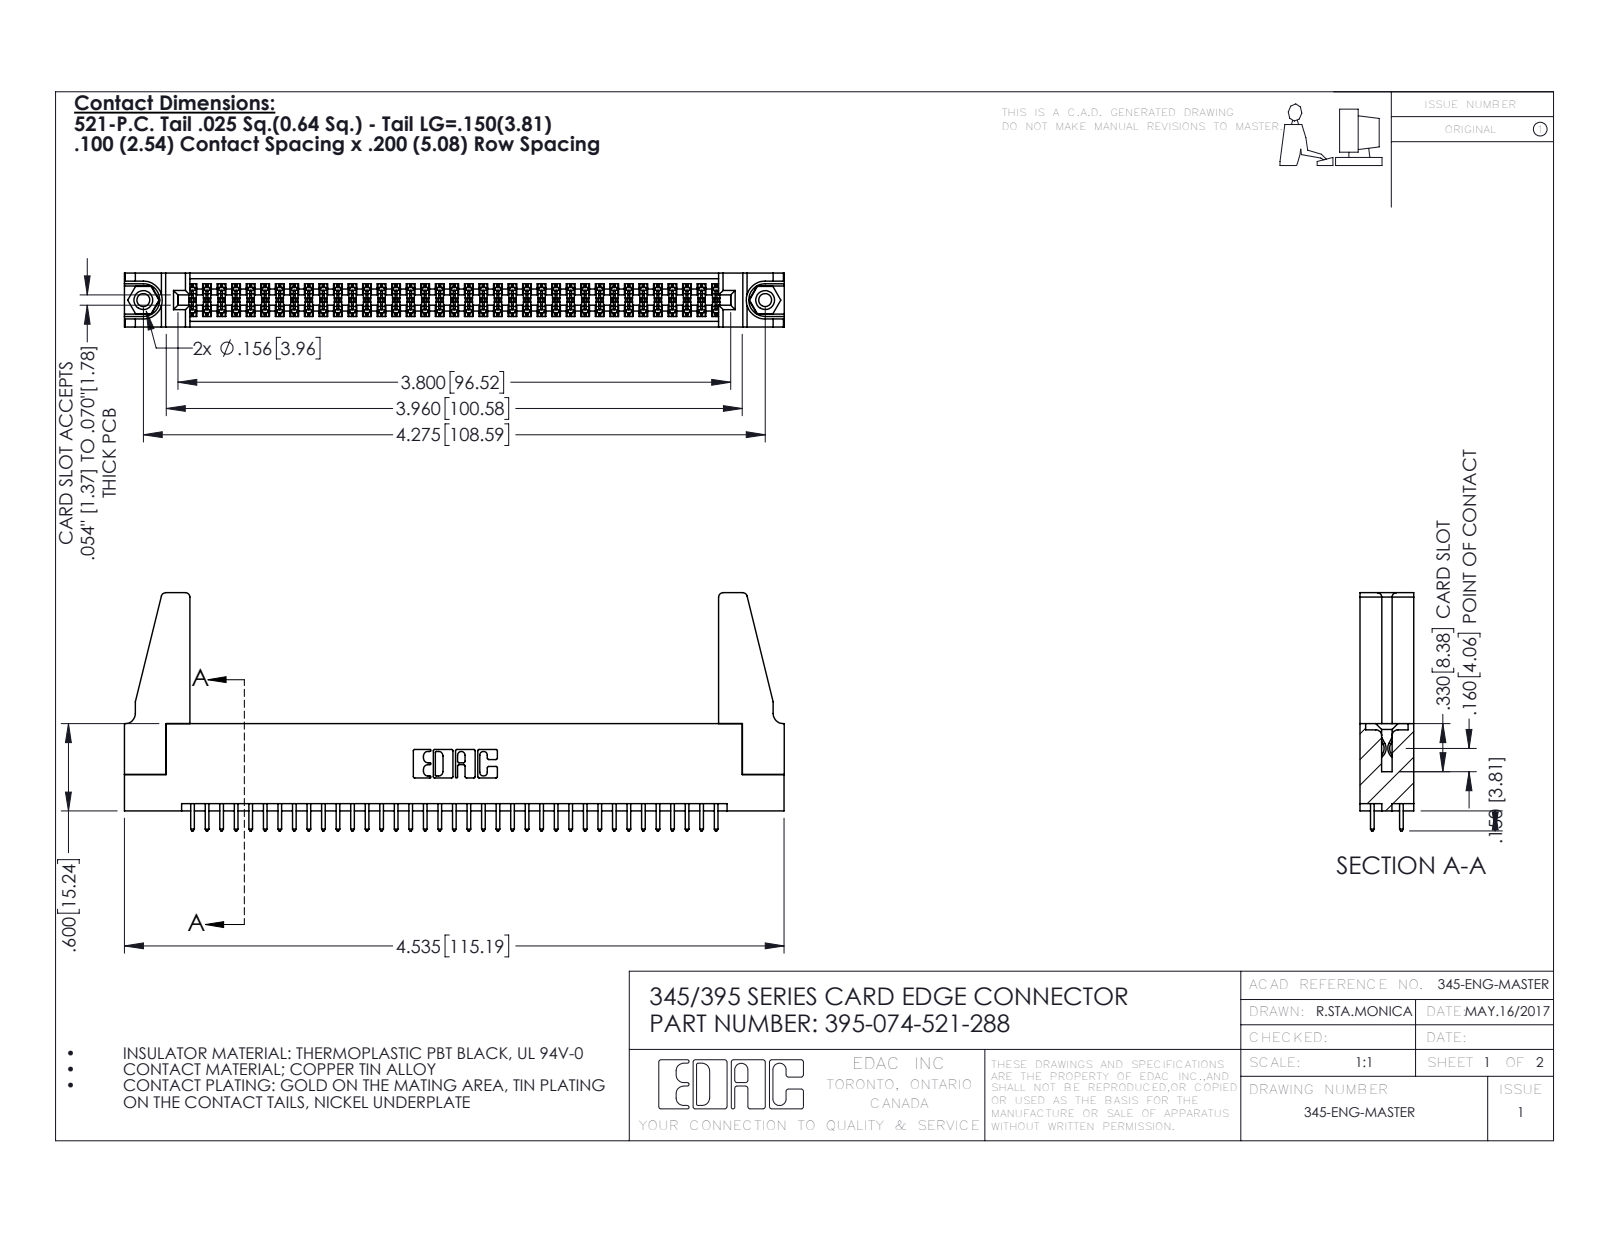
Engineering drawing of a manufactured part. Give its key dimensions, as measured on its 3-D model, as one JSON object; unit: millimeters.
{"part_name": "345-292-001_345-293-121; 345-220-078_345-220-088; 345 Part_Flush Mounting Lugs - 0.156 Dia-TH; 395-074-521-288 (+1 more)", "step_written_by": "SolidWorks 2016 (CONFIG_CONTROL_DESIGN)", "units": "millimeters", "bodies": {"solids": 79, "faces": 3950, "planar": 2594, "cylindrical": 1340, "other": 16}, "overall_size": [115.2, 41.6, 9.4], "volume_mm3": 14400, "surface_area_mm2": 19260, "round_holes": [[2.3, 2], [3.2, 2], [4, 2], [1.6, 1]], "round_bosses_or_shafts": [[3.9, 2]], "partial_cylinders_radius": [[0.2, 111], [0.3, 74], [0.3, 22], [0.8, 8], [0.2, 6], [0.8, 6], [0.7, 3], [0.4, 2]], "face_to_face_distances": [1.8, 7.6, 9.4, 5.1, 2.5, 6.9, 0.6, 5.7, 4.4, 3.8], "hole_center_spacings": [6.9, 102.6, 108.6]}
